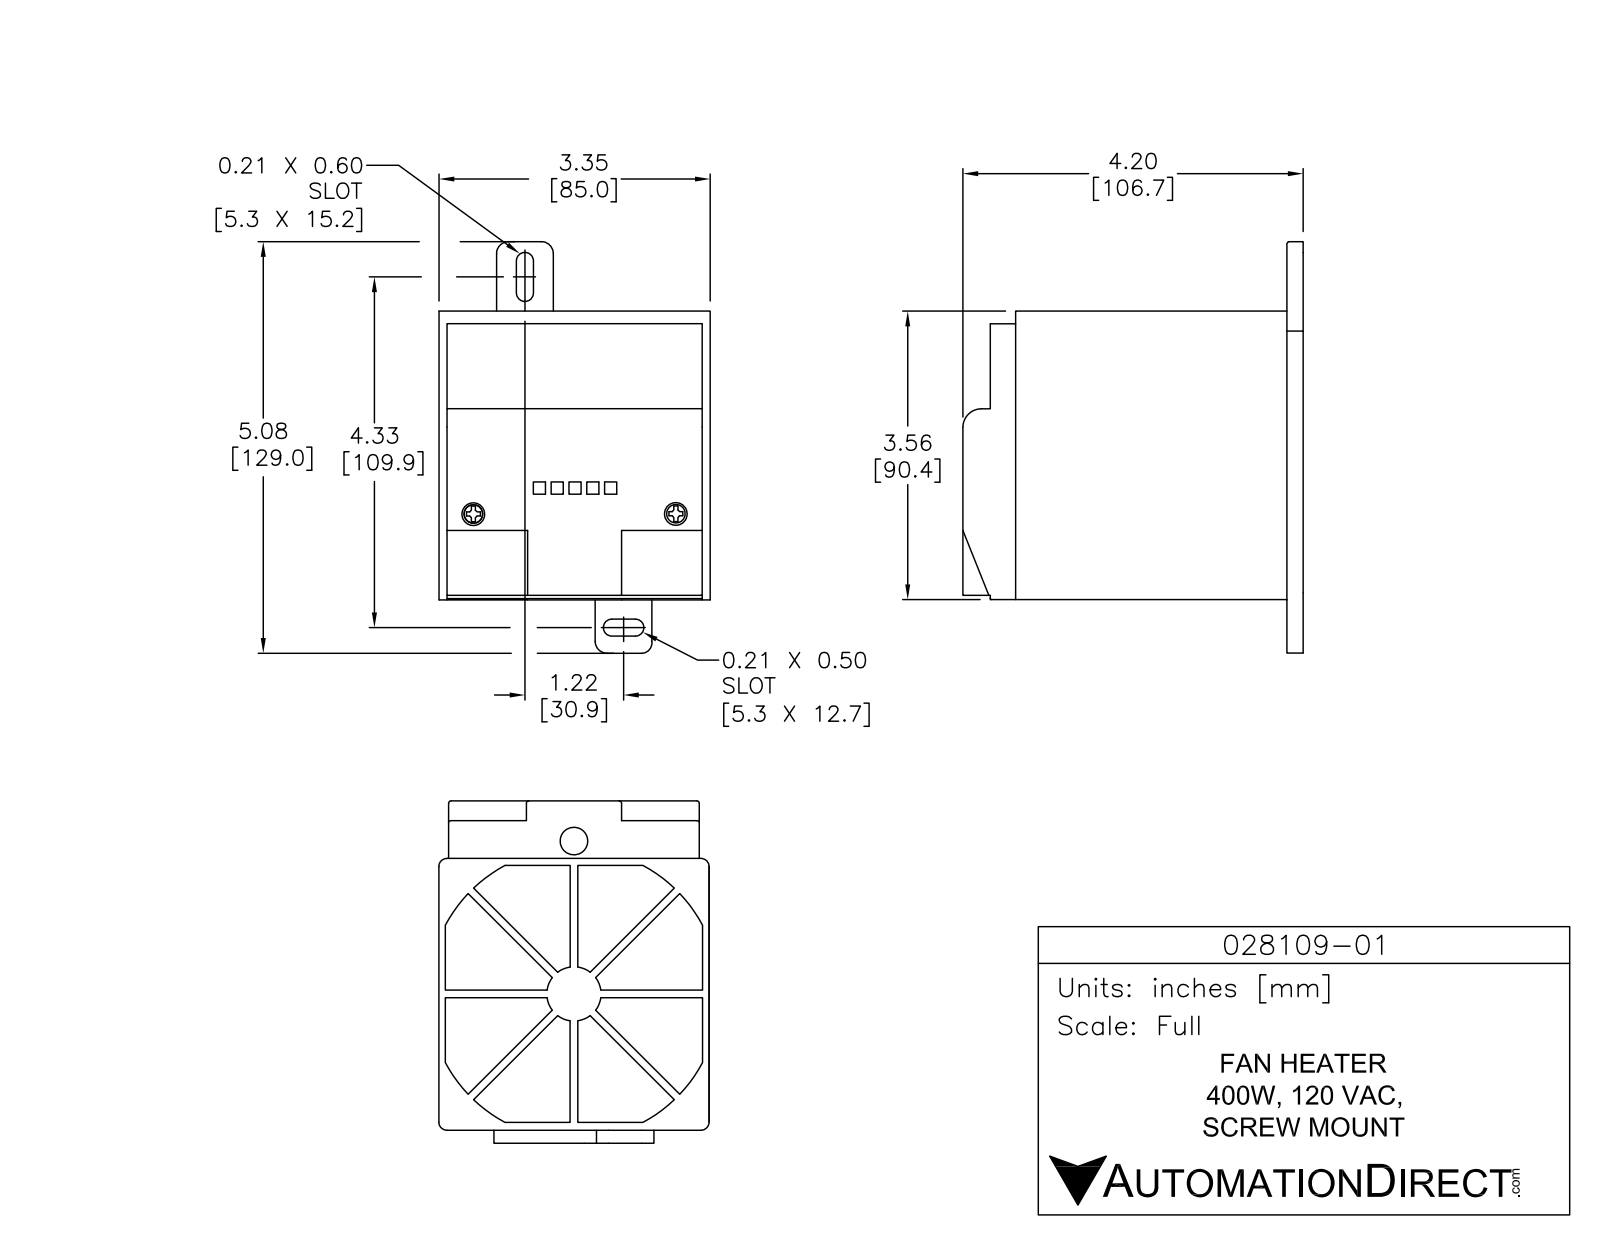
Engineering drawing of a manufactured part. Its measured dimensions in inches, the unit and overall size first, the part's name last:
Units: inches
Overall size (bounding box): 5.08 × 4.225 × 3.335
Round holes (diameter × count): ⌀0.275 ×2, ⌀0.34 ×1
Round bosses / shafts (diameter × count): ⌀0.22 ×2
Partial cylindrical surfaces — rounded edges, fillets, slot ends (radius × count): R0.065 ×60, R0.03 ×23, R0.15 ×6, R0.07 ×4, R0.1 ×4, R0.104 ×4, R0.25 ×1, R0.335 ×1
Main face-to-face distances: 3.335, 0.1, 3.455, 4.065, 3.355, 0.16, 4.225, 0.12, 3.215, 3.555
Hole centre spacings: 2.43
Volume: 45.43 in³ · Surface area: 94.92 in²
Bodies: 1 solid, 387 faces (195 planar, 164 cylindrical, 28 other)
Part name (STEP PRODUCT): 028109-01
STEP written by: SolidWorks 2013 (AUTOMOTIVE_DESIGN)
